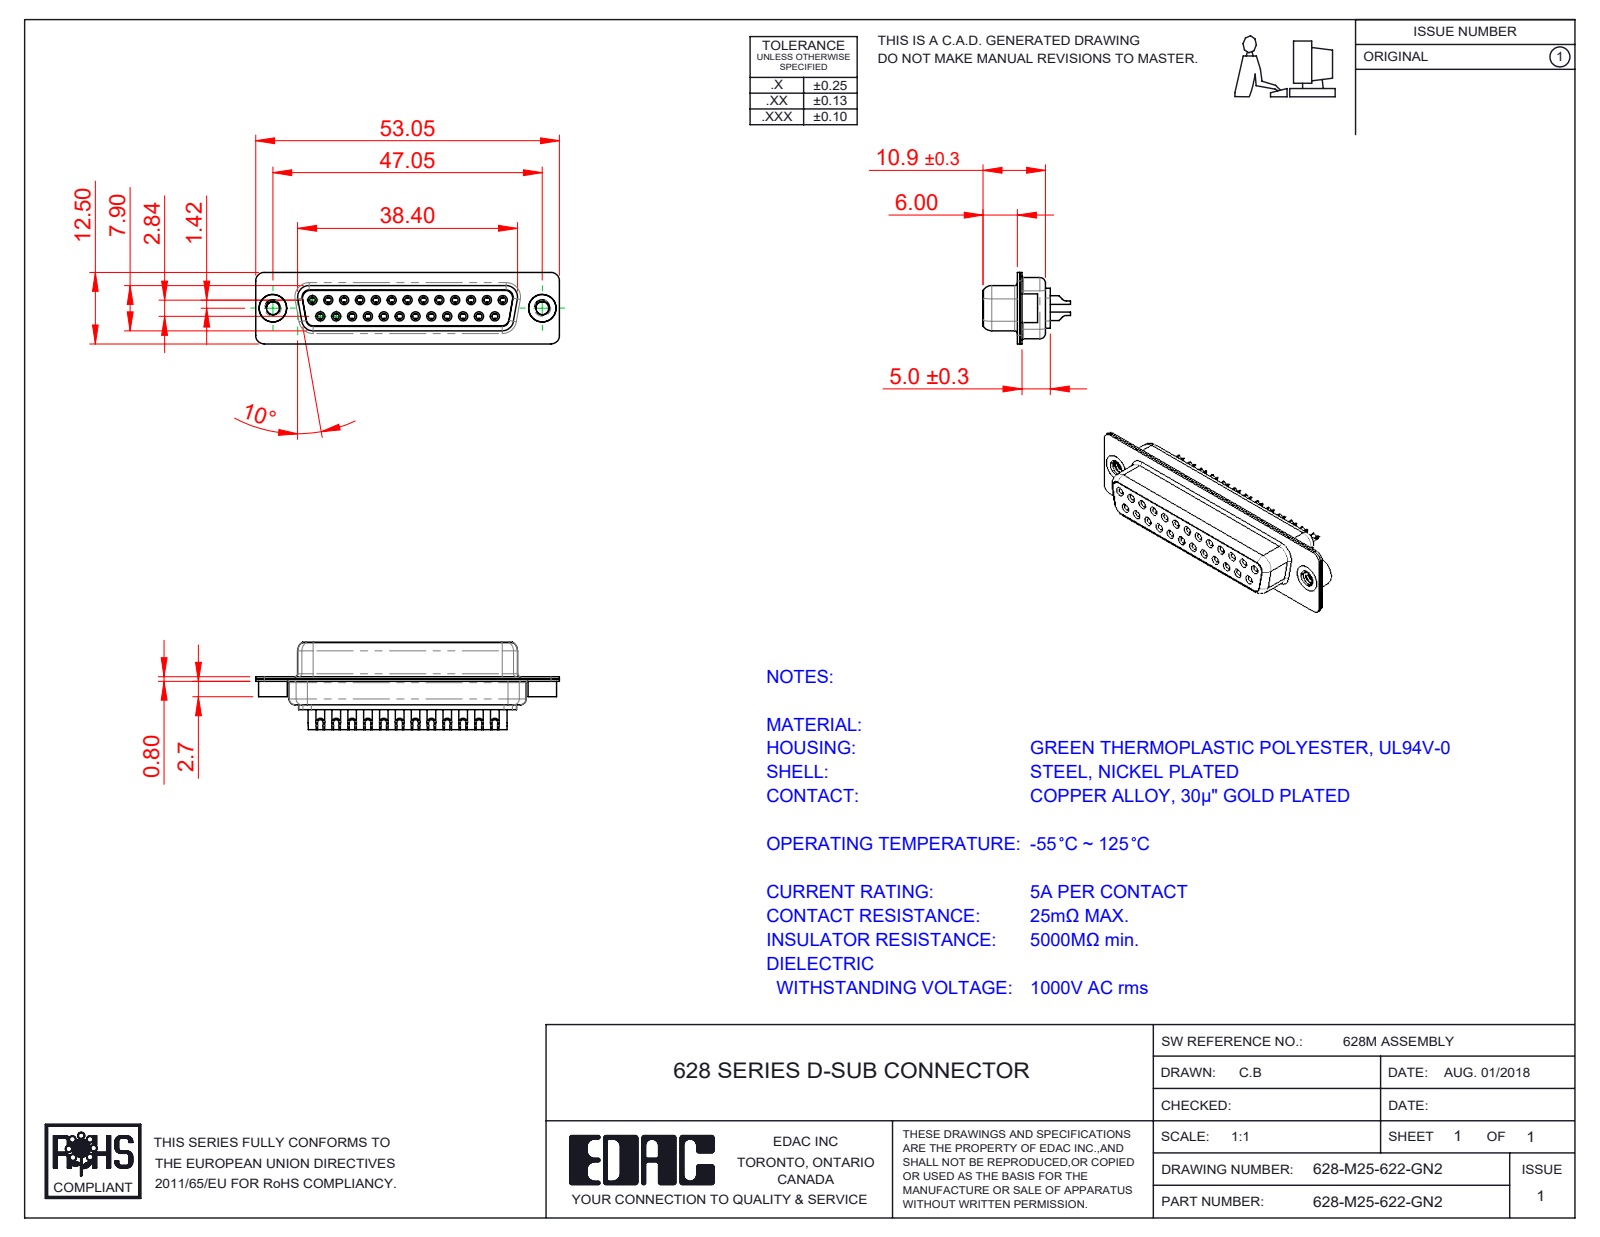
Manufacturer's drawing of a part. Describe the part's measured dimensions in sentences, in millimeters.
The part is named "628M Contact Row 1_22; 628M 4-40 Threaded Rivet; 628-M25-622-GN2; 628M Shell Rear_25 Contacts (+3 more)". Its 3-D file was written by "SolidWorks 2020 (CONFIG_CONTROL_DESIGN)". It is 30 solids with 1655 faces: 493 planar, 662 cylindrical and 500 other. Overall it measures 53.05 by 15.25 by 12.5 millimeters. Its volume is 3 776 cubic millimeters and its surface area 9 354 square millimeters. Round holes: 25 of diameter 1, 25 of diameter 1.1, 25 of diameter 1.7, 25 of diameter 1.8, 25 of diameter 2, 2 of diameter 2.26, 2 of diameter 4, 2 of diameter 4.8. Round bosses or shafts: 25 of diameter 2.2, 25 of diameter 1.6, 25 of diameter 1.5, 2 of diameter 5, 2 of diameter 4.9. Partial cylindrical surfaces (rounded edges, fillets, slot ends): 16 of radius 1.5, 12 of radius 2, 8 of radius 1.35, 8 of radius 1.6, 6 of radius 1, 4 of radius 0.25, 4 of radius 0.5, 4 of radius 0.6. The main face-to-face distances are 0.4, 1.4, 0.45, 8.45, 8.9, 1.8, 7.05, 0.85, 1, 1.85. The hole center spacings are 3.16, 2.77, 5.54, 8.31, 11.08, 13.85, 5.04, 7.49.
